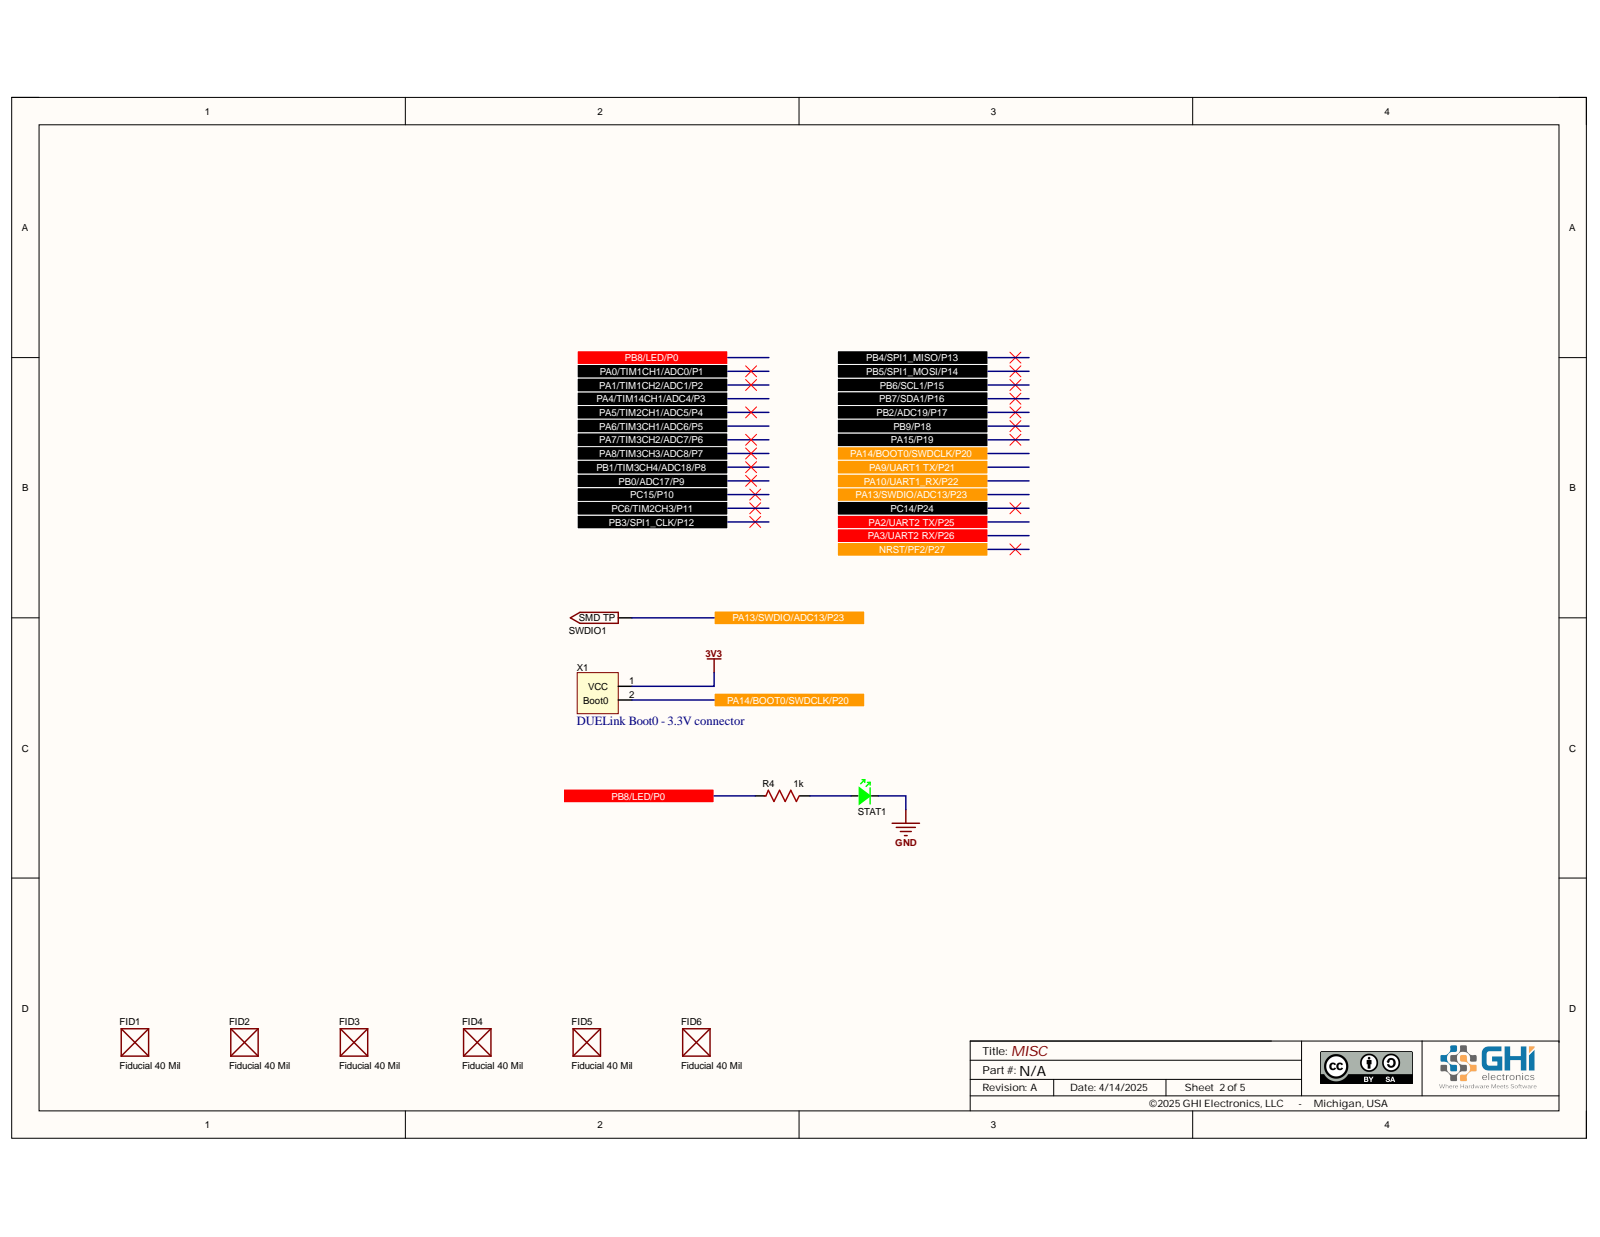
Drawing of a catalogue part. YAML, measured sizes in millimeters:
part_name: "PCB; Board; R1; User Library-R SMD 0402 (+7 more)"
step_written_by: "Open CASCADE 7.5 (AUTOMOTIVE_DESIGN)"
units: millimeters
bodies: {solids: 95, faces: 1535, planar: 1126, cylindrical: 252, other: 157}
overall_size: [32, 31.38, 22]
volume: 490
surface_area: 2443
round_holes:
  - {diameter: 3, count: 4}
  - {diameter: 1.15, count: 3}
  - {diameter: 1.02, count: 2}
partial_cylinders:
  - {radius: 0.12, count: 35}
  - {radius: 0.15, count: 14}
  - {radius: 0.18, count: 4}
  - {radius: 3.5, count: 4}
  - {radius: 0.14, count: 2}
  - {radius: 0.17, count: 2}
  - {radius: 0.18, count: 2}
face_to_face_distances: [0.5, 1.65, 1.15, 2.9, 0.45, 5.25, 0.7, 0.6, 0.75, 2.85]
hole_center_spacings: [2.54, 15, 17.62, 19.01, 25, 29.15, 5.08, 5.63]
